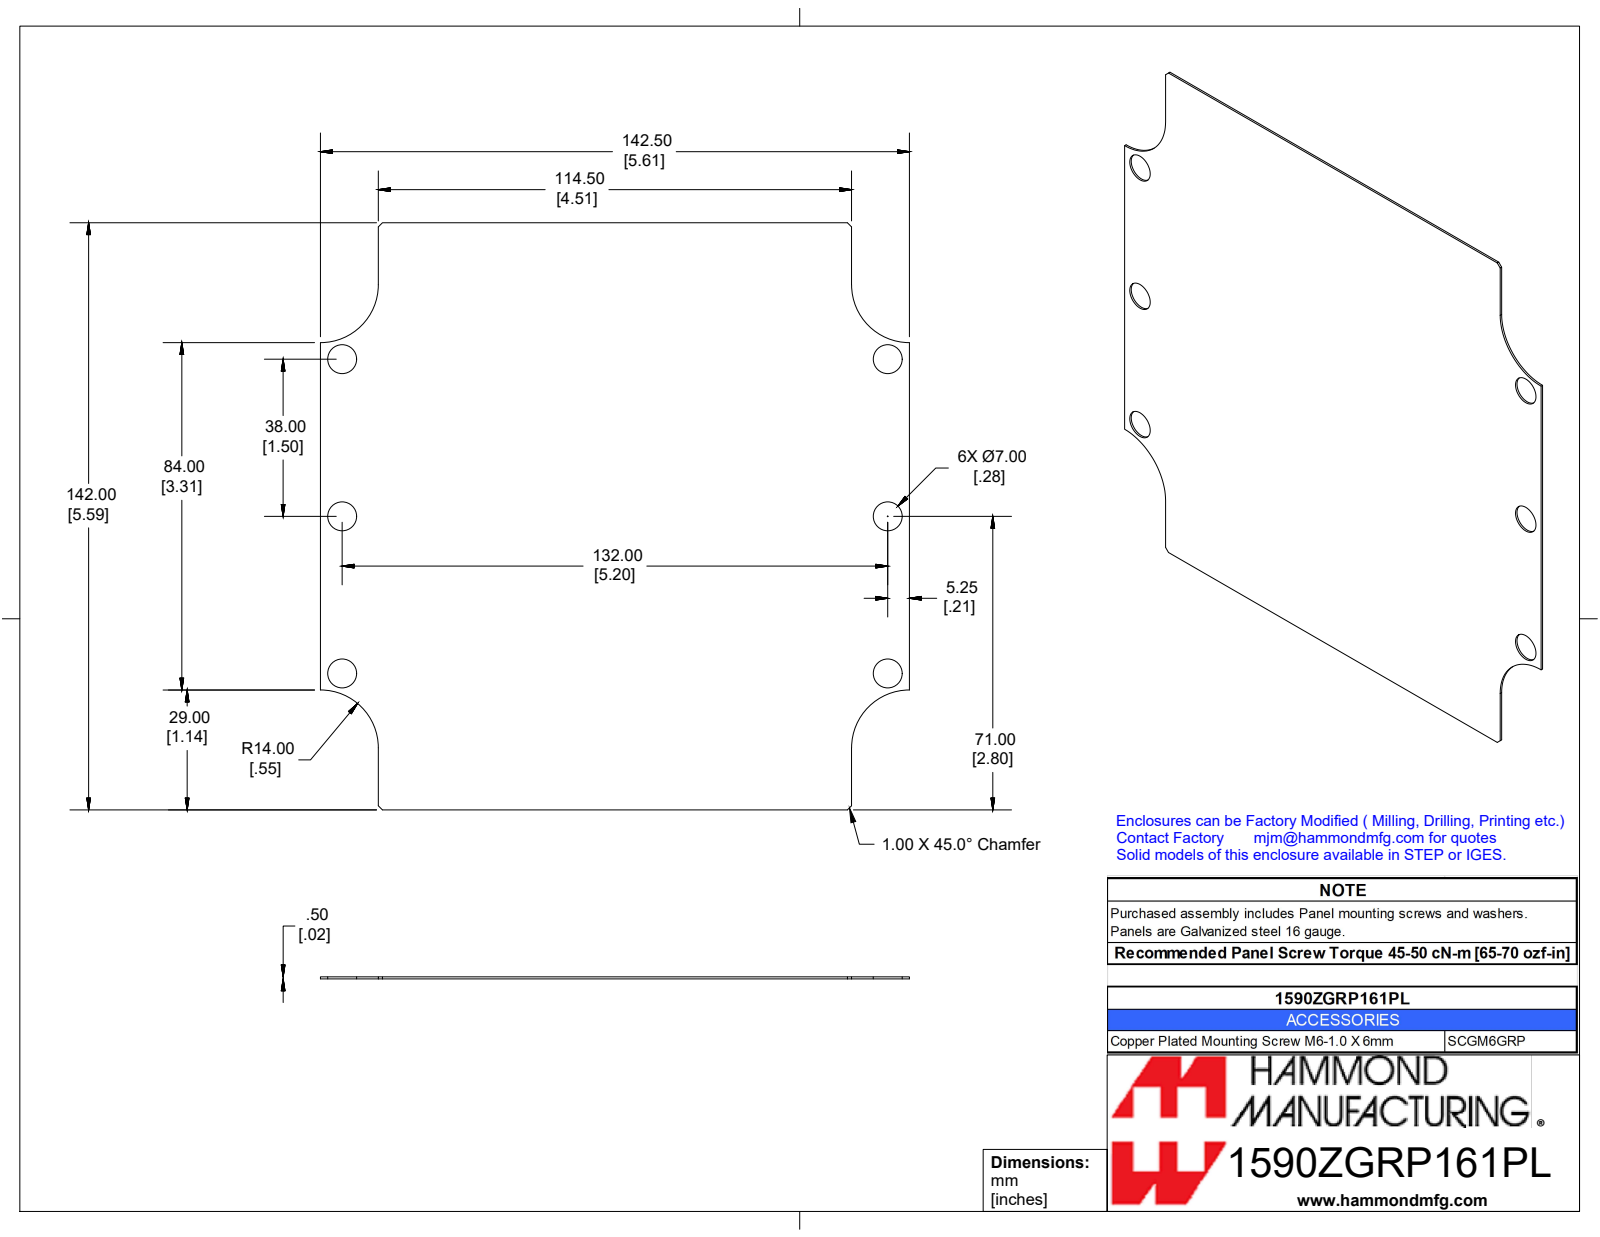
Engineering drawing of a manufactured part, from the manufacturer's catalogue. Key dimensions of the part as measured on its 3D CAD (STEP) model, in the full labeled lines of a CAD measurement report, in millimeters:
Part name (STEP PRODUCT): 1590ZGRP161PL
STEP written by: SolidWorks 2019 (CONFIG_CONTROL_DESIGN)
Units: millimetres
Bodies: 1 solid, 24 faces (14 planar, 10 cylindrical, 0 other)
Overall size (bounding box): 142.5 × 142 × 0.5
Volume: 9 280 mm³ · Surface area: 37 430 mm²
Round holes (diameter × count): ⌀7 ×6
Partial cylindrical surfaces — rounded edges, fillets, slot ends (radius × count): R14 ×4
Main face-to-face distances: 0.5, 142, 142.5, 14, 128.5, 114.5, 179.9, 179.9
Hole centre spacings: 38, 137.4, 132, 76, 152.3
